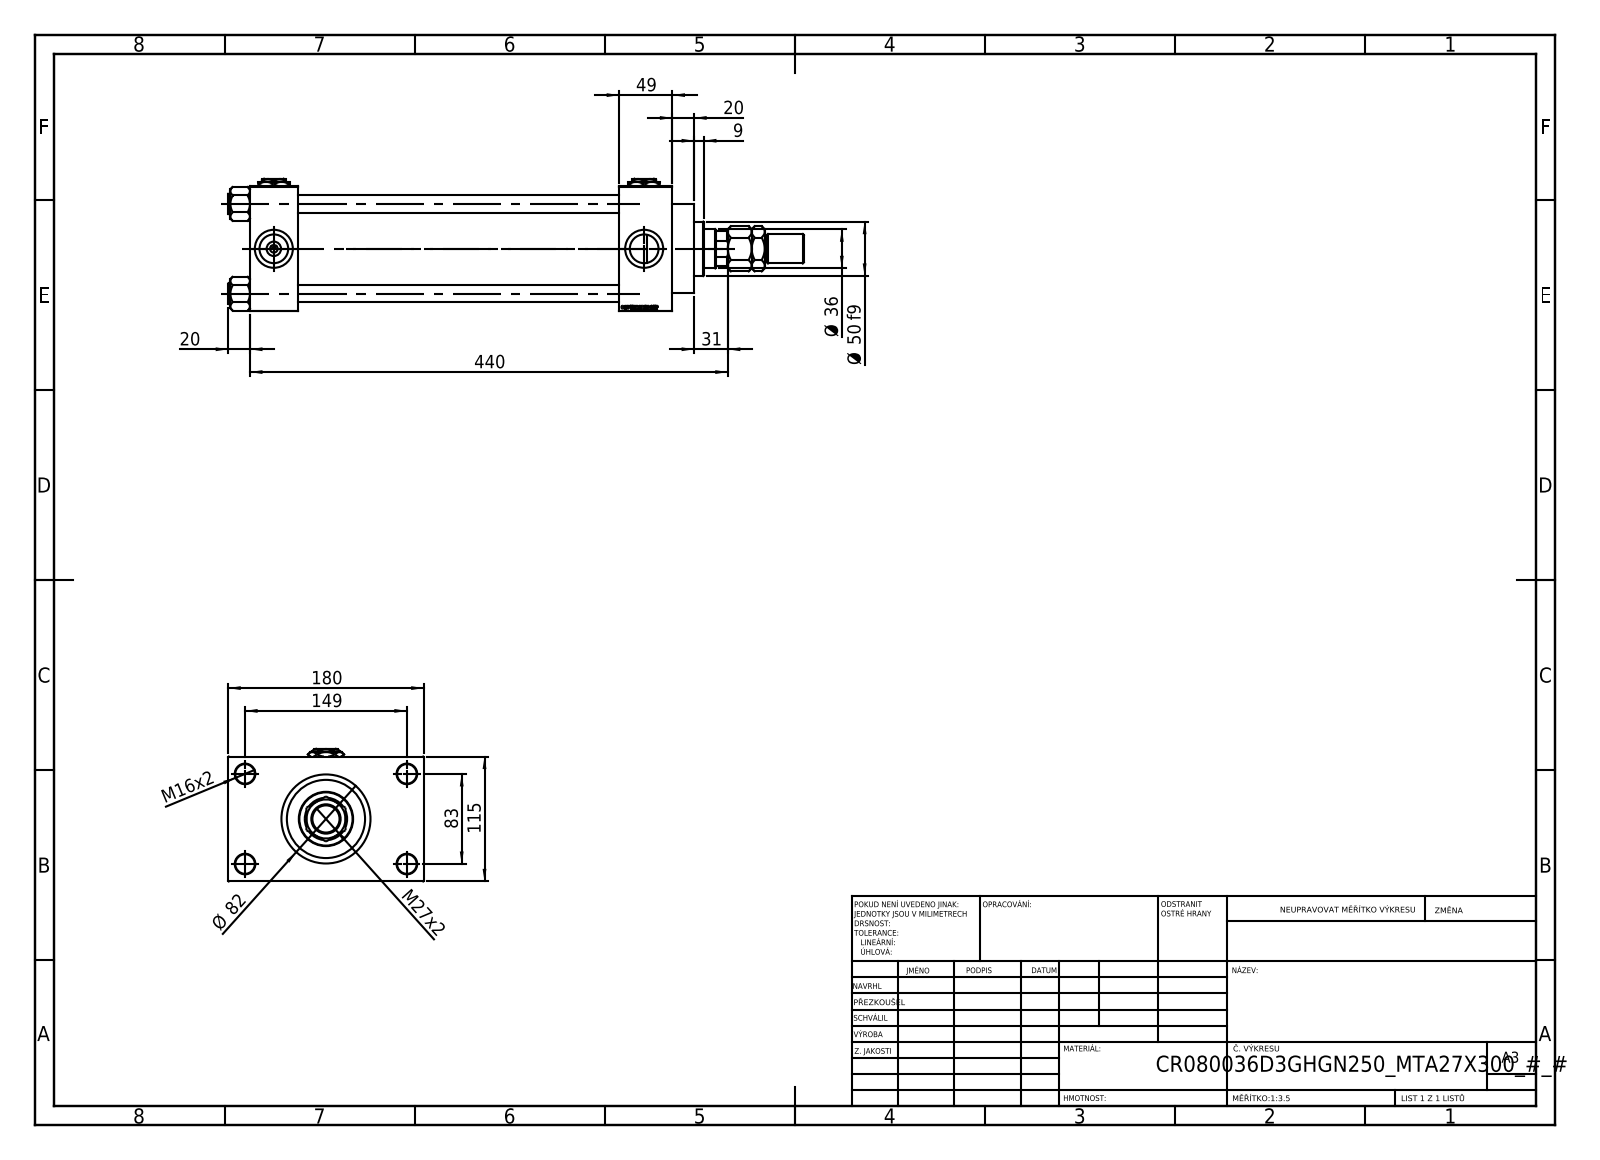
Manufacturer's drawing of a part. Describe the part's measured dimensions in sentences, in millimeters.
The part is named "V215CR_D_TYCINKA; V215CR_D_Body; NUT_M5_D; V215CR_VCP_D (+3 more)". Its 3-D file was written by "SolidWorks 2019 (CONFIG_CONTROL_DESIGN)". It is 14 solids with 1301 faces: 608 planar, 103 cylindrical and 590 other. Overall it measures 530 by 180 by 122 millimeters. Its volume is 2 623 000 cubic millimeters and its surface area 504 967 square millimeters. Round holes: 4 of diameter 16, 4 of diameter 18, 4 of diameter 26.44, 4 of diameter 35, 3 of diameter 7, 1 of diameter 25.5, 1 of diameter 36, 1 of diameter 39, 1 of diameter 61, 1 of diameter 72, 1 of diameter 80. Round bosses or shafts: 4 of diameter 19, 1 of diameter 86, 1 of diameter 82, 1 of diameter 50, 1 of diameter 27, 1 of diameter 25. Partial cylindrical surfaces (rounded edges, fillets, slot ends): 1 of radius 17.5. The main face-to-face distances are 115, 296, 345, 49, 44, 340, 389, 32.5, 147.5, 180. The hole center spacings are 33.15, 58.48, 82.7, 85.28, 89.24, 115.85, 142.43, 83.
